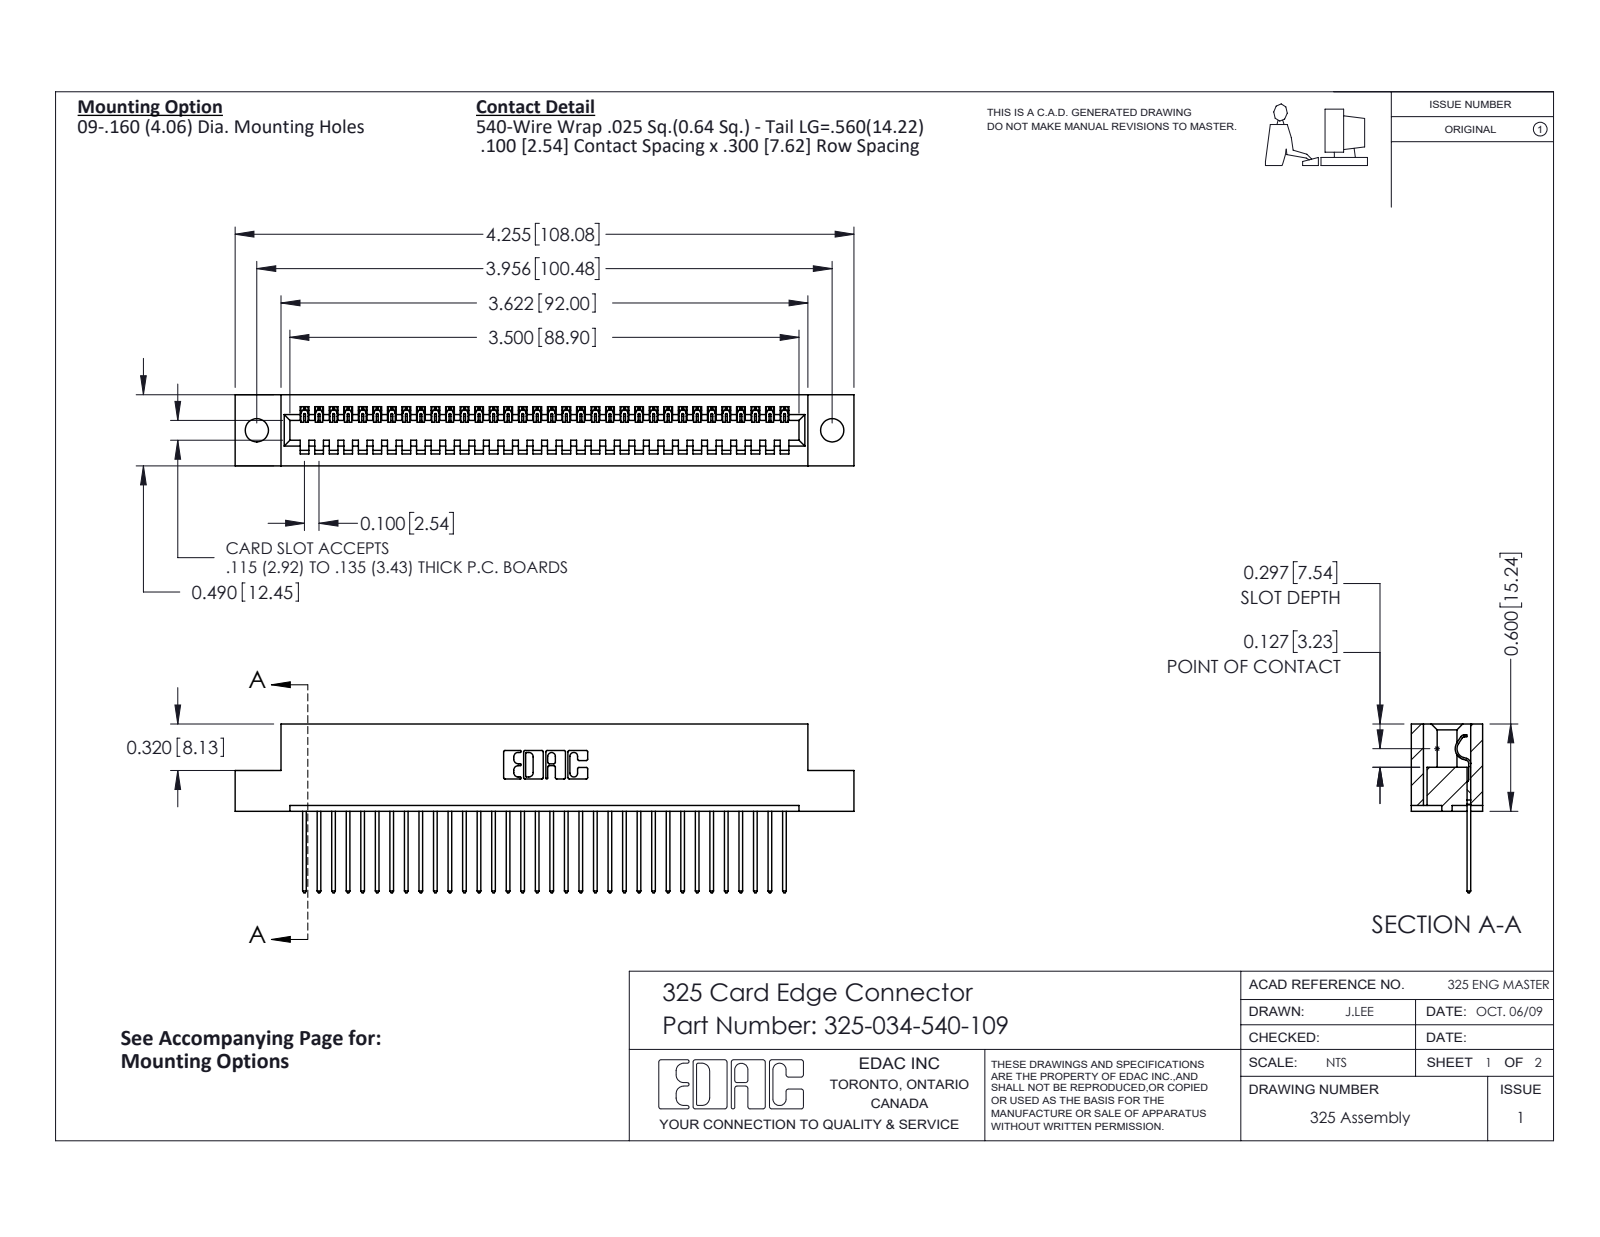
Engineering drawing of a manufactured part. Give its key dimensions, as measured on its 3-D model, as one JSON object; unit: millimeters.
{"part_name": "325-292-001_325-293-140; 325-034-540-109; 325 Part_.160 TH", "step_written_by": "SolidWorks 2016 (CONFIG_CONTROL_DESIGN)", "units": "millimeters", "bodies": {"solids": 35, "faces": 2086, "planar": 1498, "cylindrical": 588, "other": 0}, "overall_size": [108.1, 29.5, 12.4], "volume_mm3": 13500, "surface_area_mm2": 14820, "round_holes": [[4.1, 2]], "partial_cylinders_radius": [[0.2, 68], [0.3, 68], [0.3, 22], [0.2, 6], [0.8, 6], [0.7, 3], [0.4, 1], [0.6, 1]], "face_to_face_distances": [2.1, 10.3, 12.4, 7.6, 2.7, 9.7, 0.6, 8.3, 1, 14.2], "hole_center_spacings": [100.5]}
